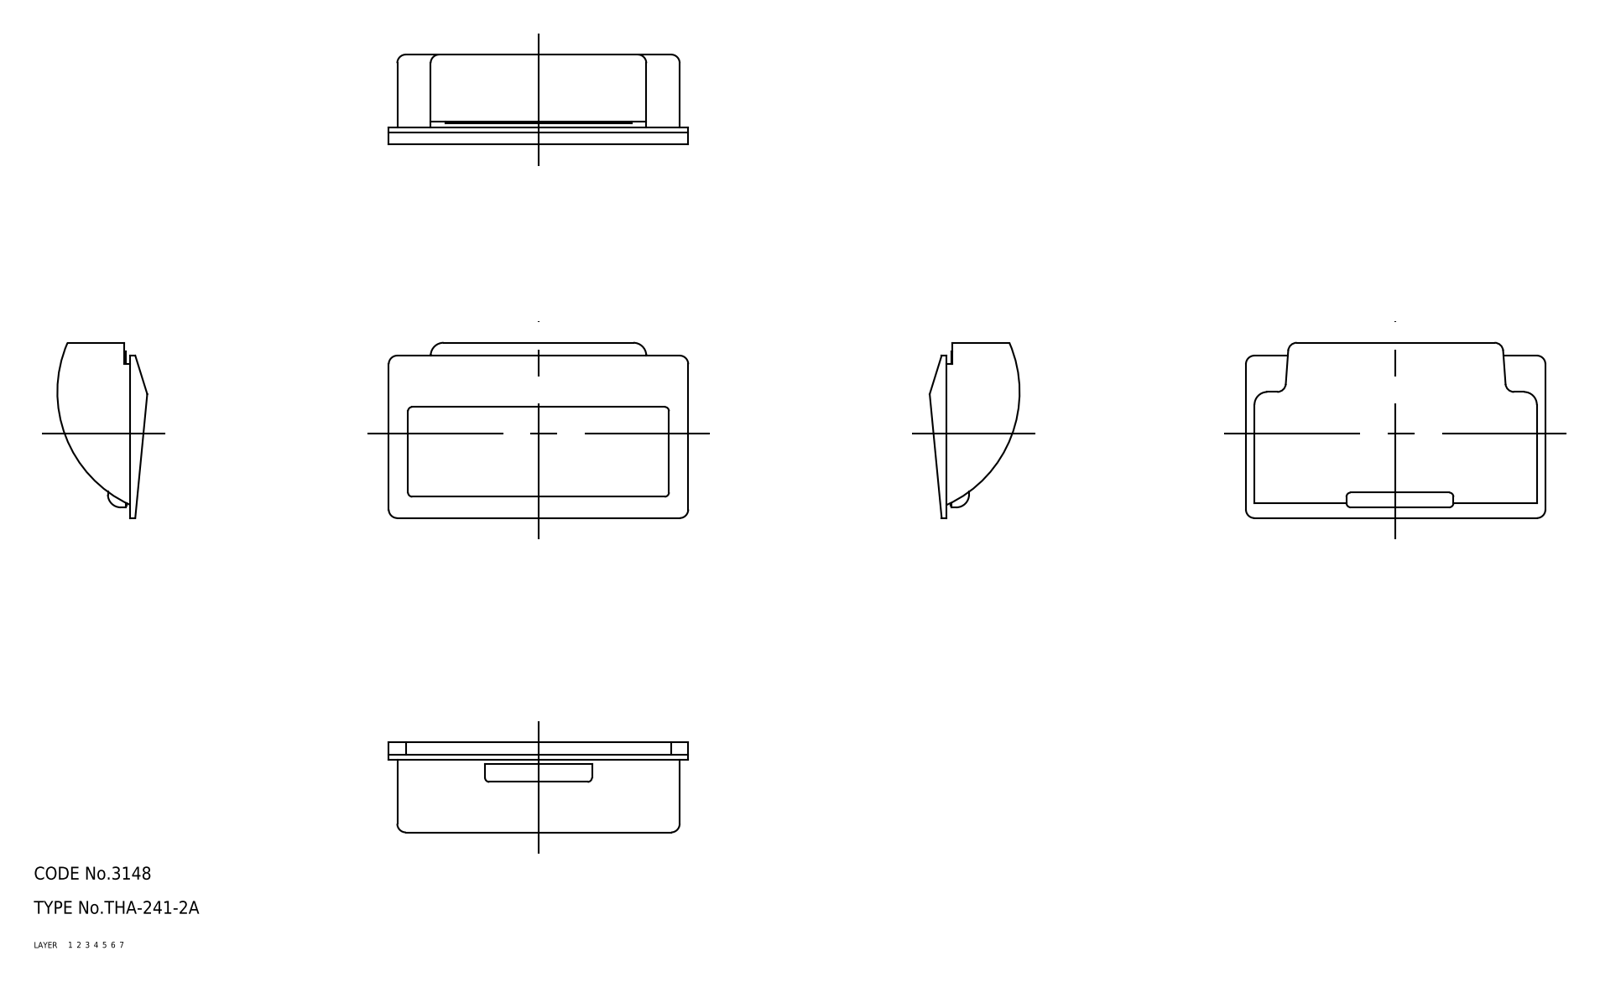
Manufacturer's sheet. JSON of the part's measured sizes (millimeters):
{"part_name": "67114085", "step_written_by": "CADfix (AUTOMOTIVE_DESIGN)", "units": "millimeters", "bodies": {"solids": 1, "faces": 91, "planar": 0, "cylindrical": 0, "other": 91}, "overall_size": [70, 41, 21], "volume_mm3": 14378, "surface_area_mm2": 11741}
